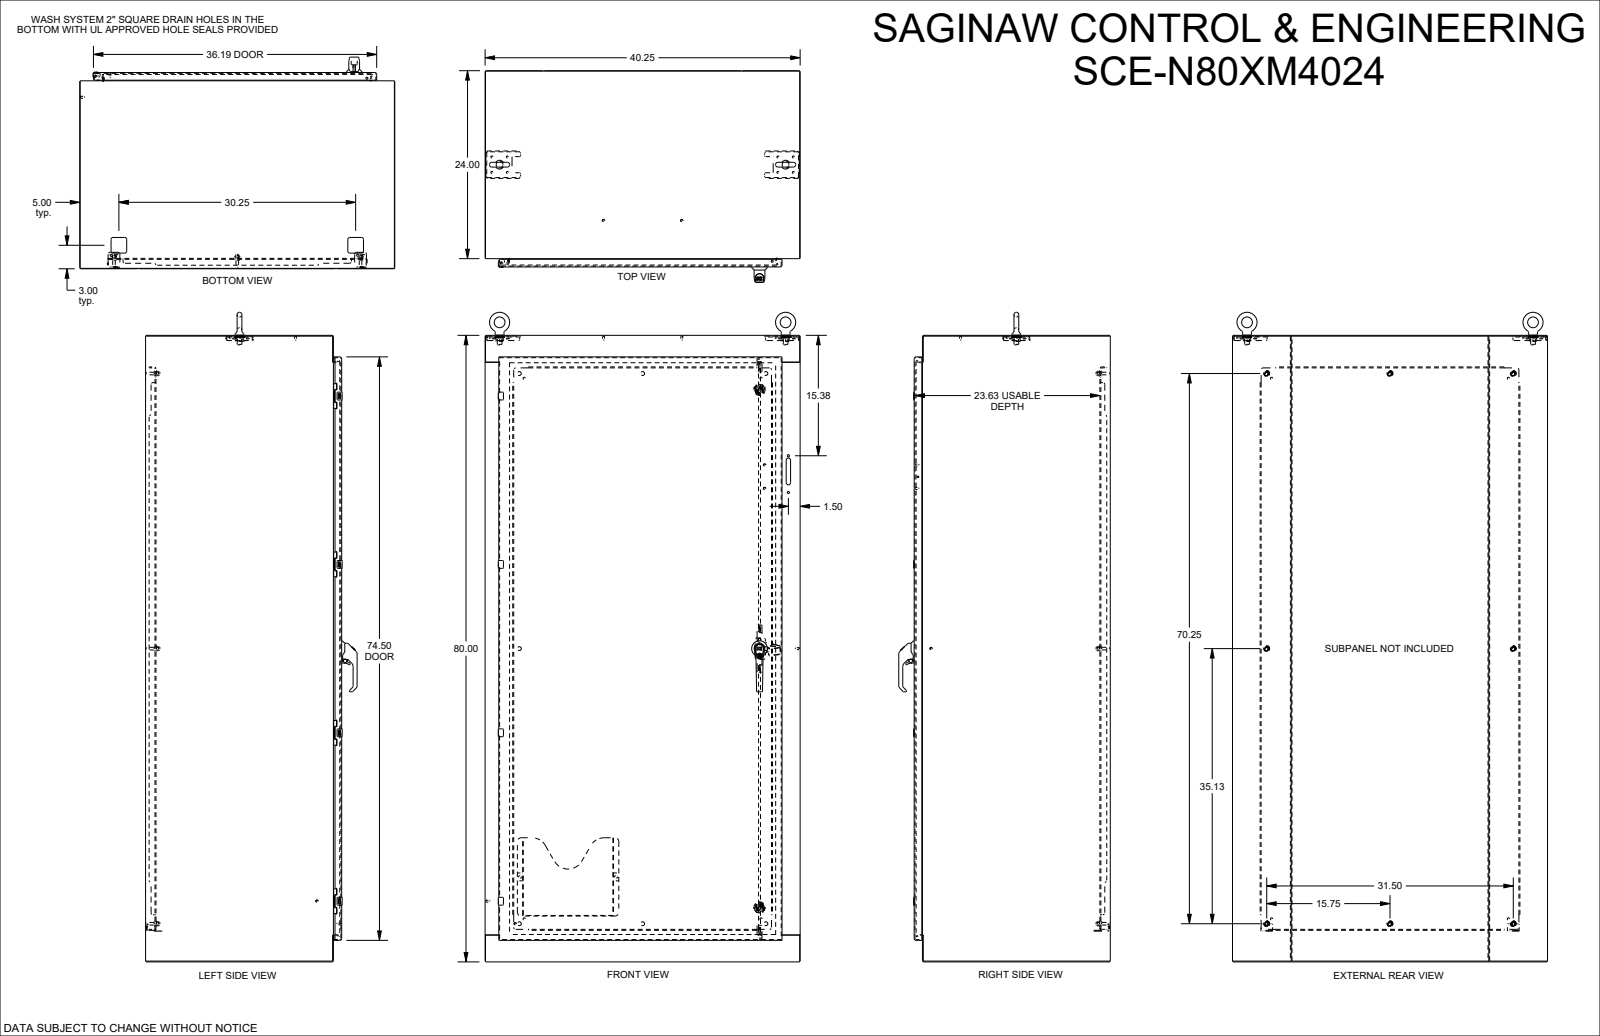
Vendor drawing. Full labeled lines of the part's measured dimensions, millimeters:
Part name (STEP PRODUCT): SCE-N80XM4024
STEP written by: SolidWorks 2023 (AUTOMOTIVE_DESIGN)
Units: millimetres
Bodies: 22 solids, 3150 faces (1335 planar, 1027 cylindrical, 788 other)
Overall size (bounding box): 2106.8 × 1022.4 × 687
Volume: 22 530 000 mm³ · Surface area: 16 980 000 mm²
Round holes (diameter × count): ⌀6.4 ×10, ⌀5.2 ×8, ⌀6.2 ×8, ⌀9.5 ×8, ⌀1 ×4, ⌀4.3 ×4, ⌀5.5 ×4, ⌀6.5 ×4, ⌀7.1 ×2, ⌀8.7 ×2, ⌀9.1 ×2, ⌀22.2 ×2
Round bosses / shafts (diameter × count): ⌀4.3 ×12, ⌀6.4 ×8, ⌀6.1 ×8, ⌀5 ×5, ⌀35.6 ×2, ⌀29.8 ×2, ⌀15.2 ×2, ⌀8.7 ×2
Partial cylindrical surfaces — rounded edges, fillets, slot ends (radius × count): R0.8 ×96, R0.4 ×68, R1 ×37, R3.2 ×31, R0.5 ×24, R1.6 ×24, R1 ×22, R2 ×21
Main face-to-face distances: 2.6, 633.8, 2.6, 1019.7, 631.2, 636.5, 1022.4, 2029.4, 1017.1, 607
Hole centre spacings: 546.1, 1092.2, 12.5, 12.5, 25, 35.5, 35.6, 50.3
